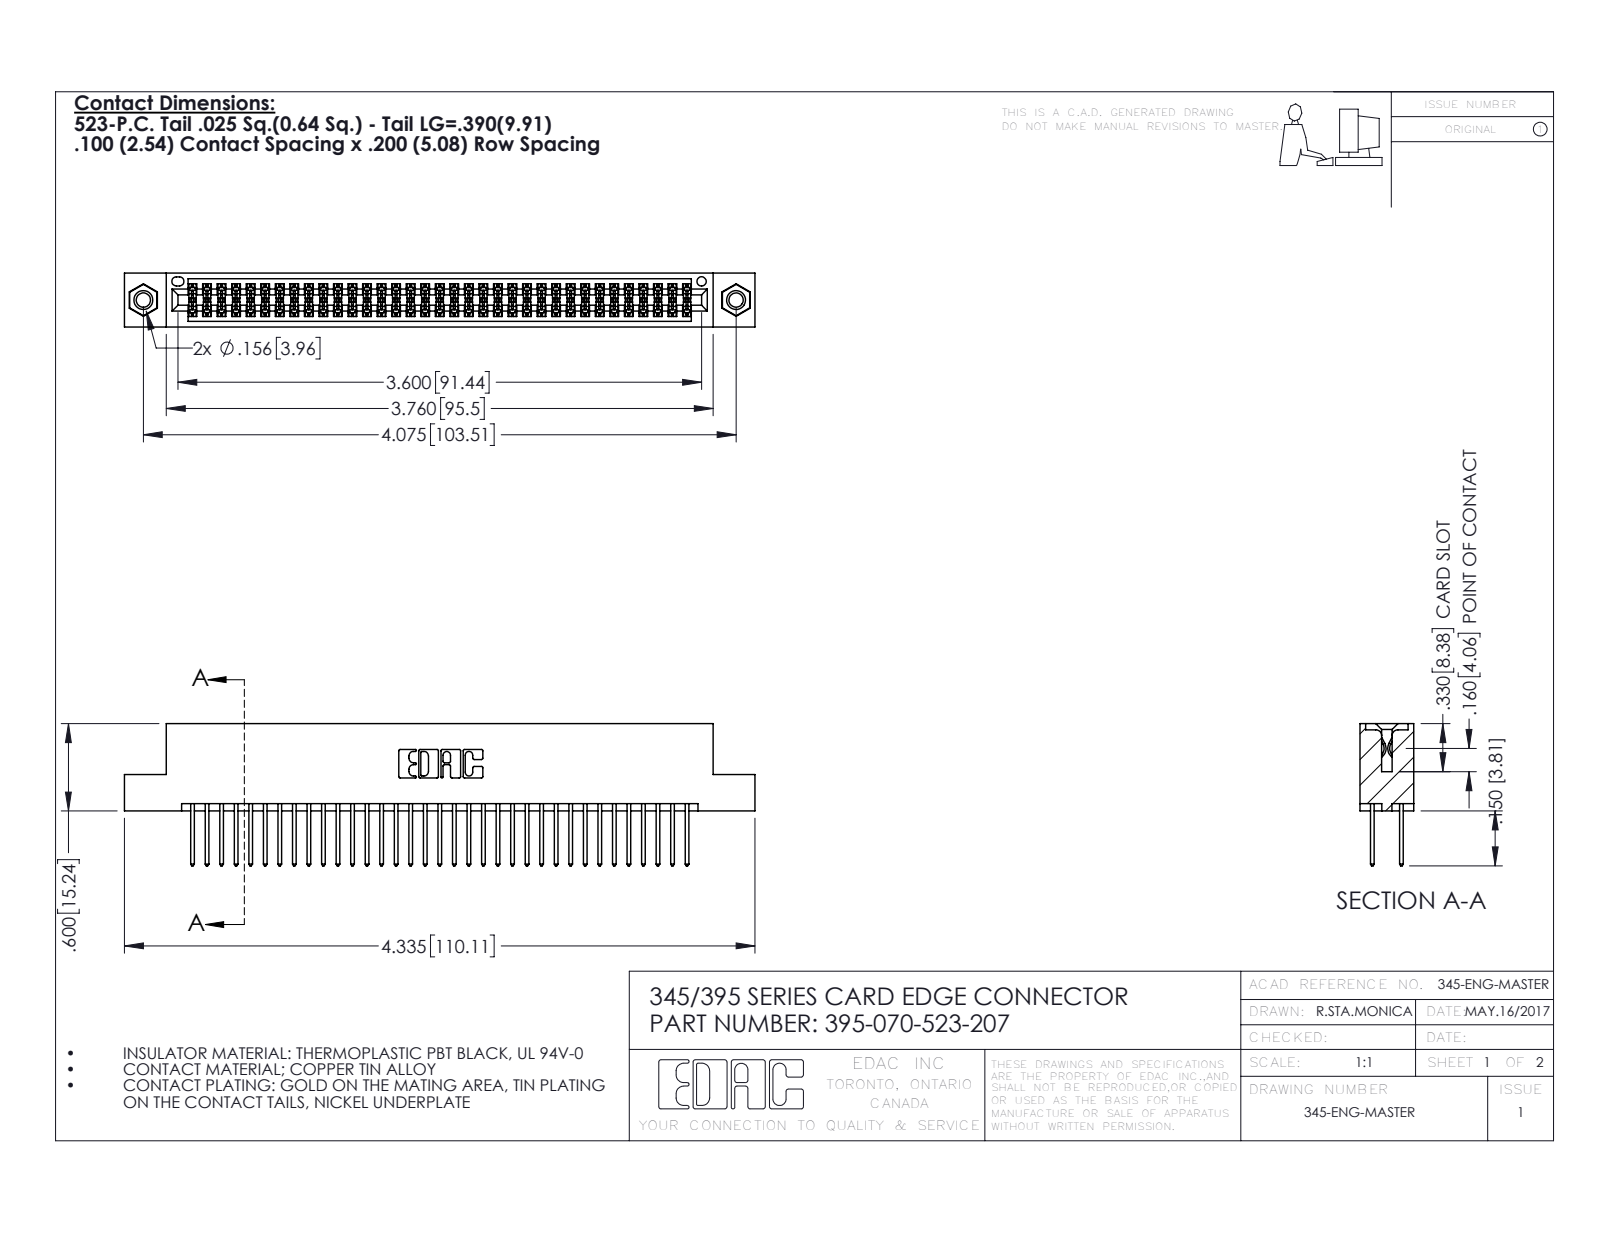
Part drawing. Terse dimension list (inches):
name: 345 Part_Flush Mounting Lugs - 0.156 Dia-TI; 395-070-523-207; 345-250-001_345-250-005-103; 345-292-001_345-293-123
written by: SolidWorks 2016 (CONFIG_CONTROL_DESIGN)
unit: in
bodies: 73 solids, 3686 faces (2422 planar, 1248 cylindrical, 16 other)
size: 4.335 × 0.977 × 0.37
volume: 0.657 in³; area: 25.49 in²
holes: 2× ⌀0.098, 2× ⌀0.125, 2× ⌀0.156, 1× ⌀0.064
bosses: 2× ⌀0.155
rounds: 105× R0.006, 70× R0.01, 22× R0.01, 6× R0.007, 6× R0.031, 3× R0.026, 2× R0.014, 2× R0.019
face distances: 0.072, 0.298, 0.2, 0.098, 0.272, 0.025, 0.37, 0.225, 0.175, 0.149
hole spacings: 0.27, 3.839, 4.075
